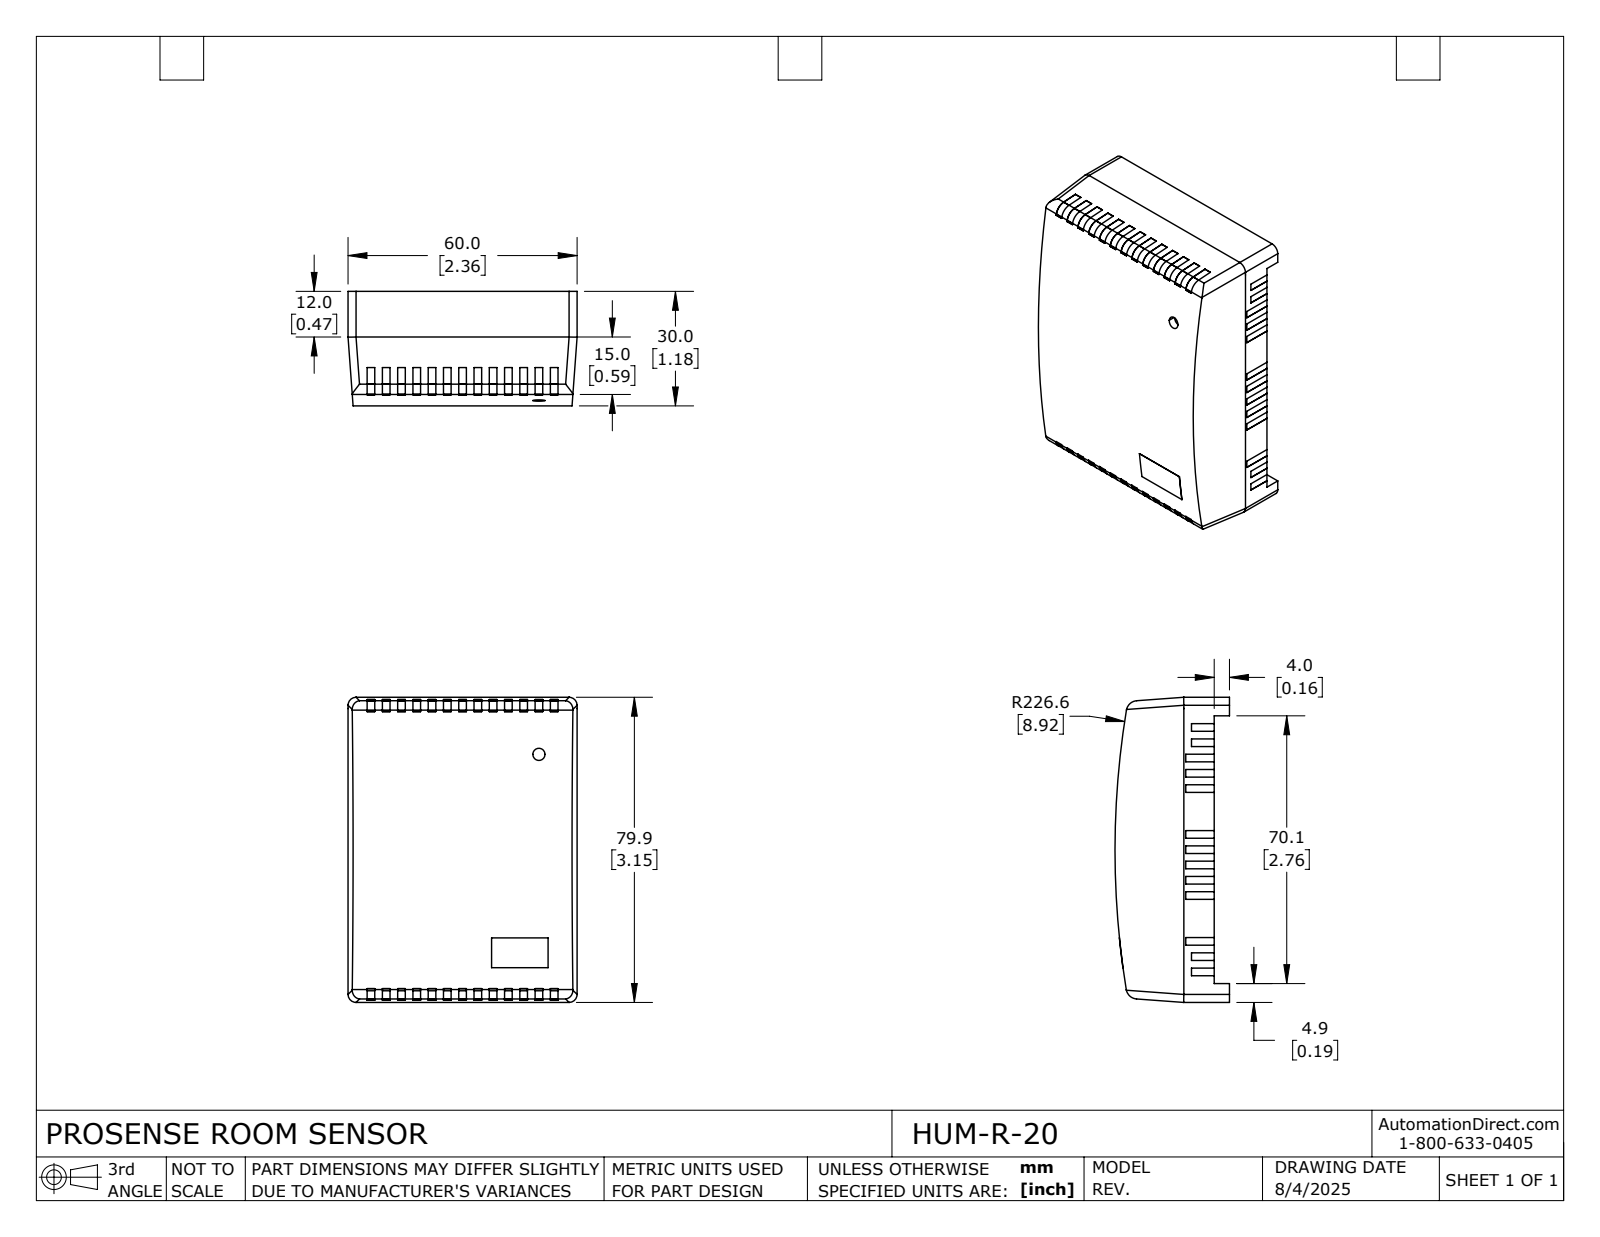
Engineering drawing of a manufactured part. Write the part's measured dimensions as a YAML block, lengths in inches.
part_name: "HUM-R-20"
step_written_by: "SolidWorks 2024 (AUTOMOTIVE_DESIGN)"
units: inches
bodies: {solids: 1, faces: 461, planar: 354, cylindrical: 105, other: 2}
overall_size: [3.146, 2.362, 1.181]
volume: 7.228
surface_area: 26.46
partial_cylinders:
  - {radius: 0.083, count: 8}
  - {radius: 8.919, count: 3}
  - {radius: 0.082, count: 2}
  - {radius: 0.115, count: 2}
  - {radius: 0.116, count: 2}
  - {radius: 8.919, count: 1}
face_to_face_distances: [3.146, 0.157, 2.362, 2.362, 0.957, 0.799, 0.194, 2.954, 2.76, 2.951]
